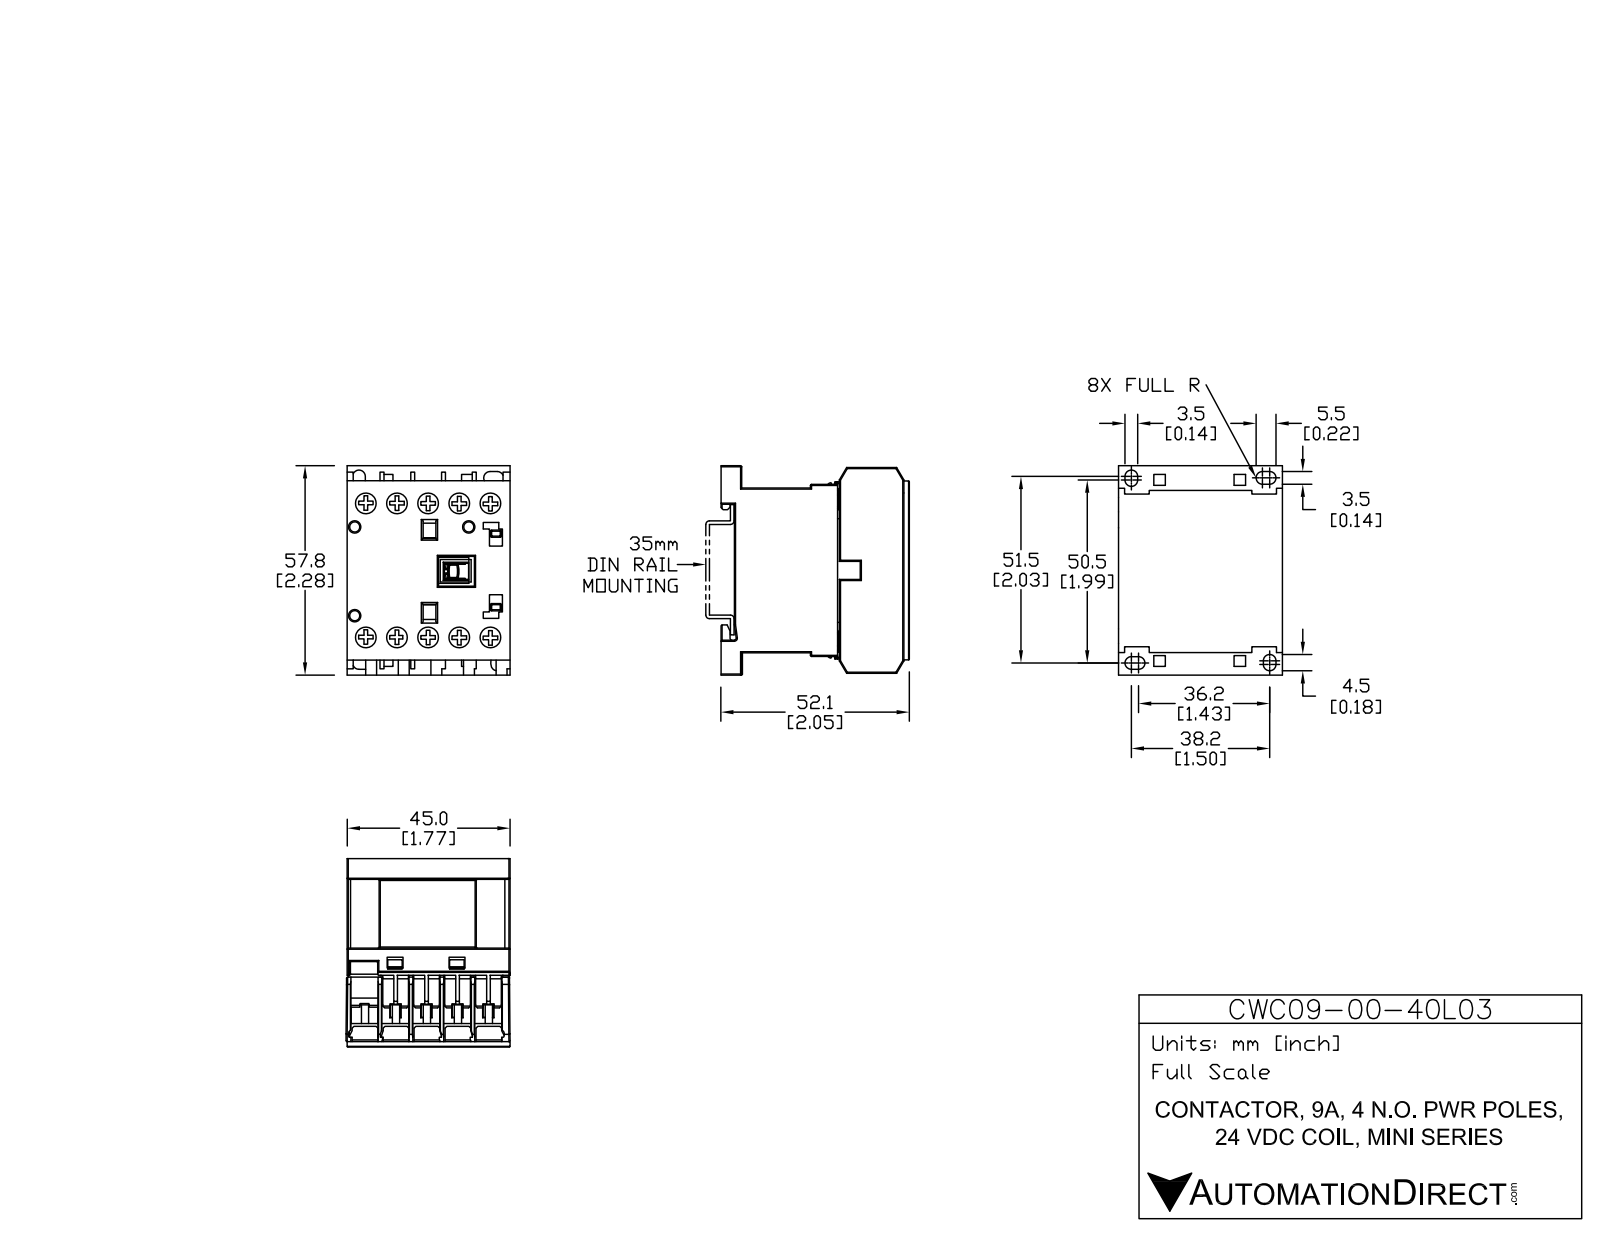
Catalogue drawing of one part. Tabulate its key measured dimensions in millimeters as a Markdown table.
| quantity | value |
| --- | --- |
| part name | CWC09-00-40L03 |
| STEP written by | SolidWorks 2013 (AUTOMOTIVE_DESIGN) |
| units | millimeters |
| bodies | 15 solids, 535 faces (445 planar, 90 cylindrical, 0 other) |
| overall size | 58.04 × 52.12 × 45.75 |
| volume | 97 133 mm³ |
| surface area | 30 437 mm² |
| round holes (diameter × count) | 6.2 × 10, 2.8 × 3 |
| round bosses / shafts (diameter × count) | 5.9 × 10 |
| partial cylindrical surfaces (radius × count) | 0.3 × 20, 1.72 × 6, 1.73 × 2, 0.32 × 1, 0.42 × 1, 0.55 × 1 |
| main face-to-face distances | 8.25, 45.5, 1.25, 16.5, 9.5, 5.5, 17.75, 5.13, 10.63, 7 |
| hole center spacings | 8.55, 37.94, 17.1, 40.72, 36.96, 25.65, 44.99, 6.91 |
